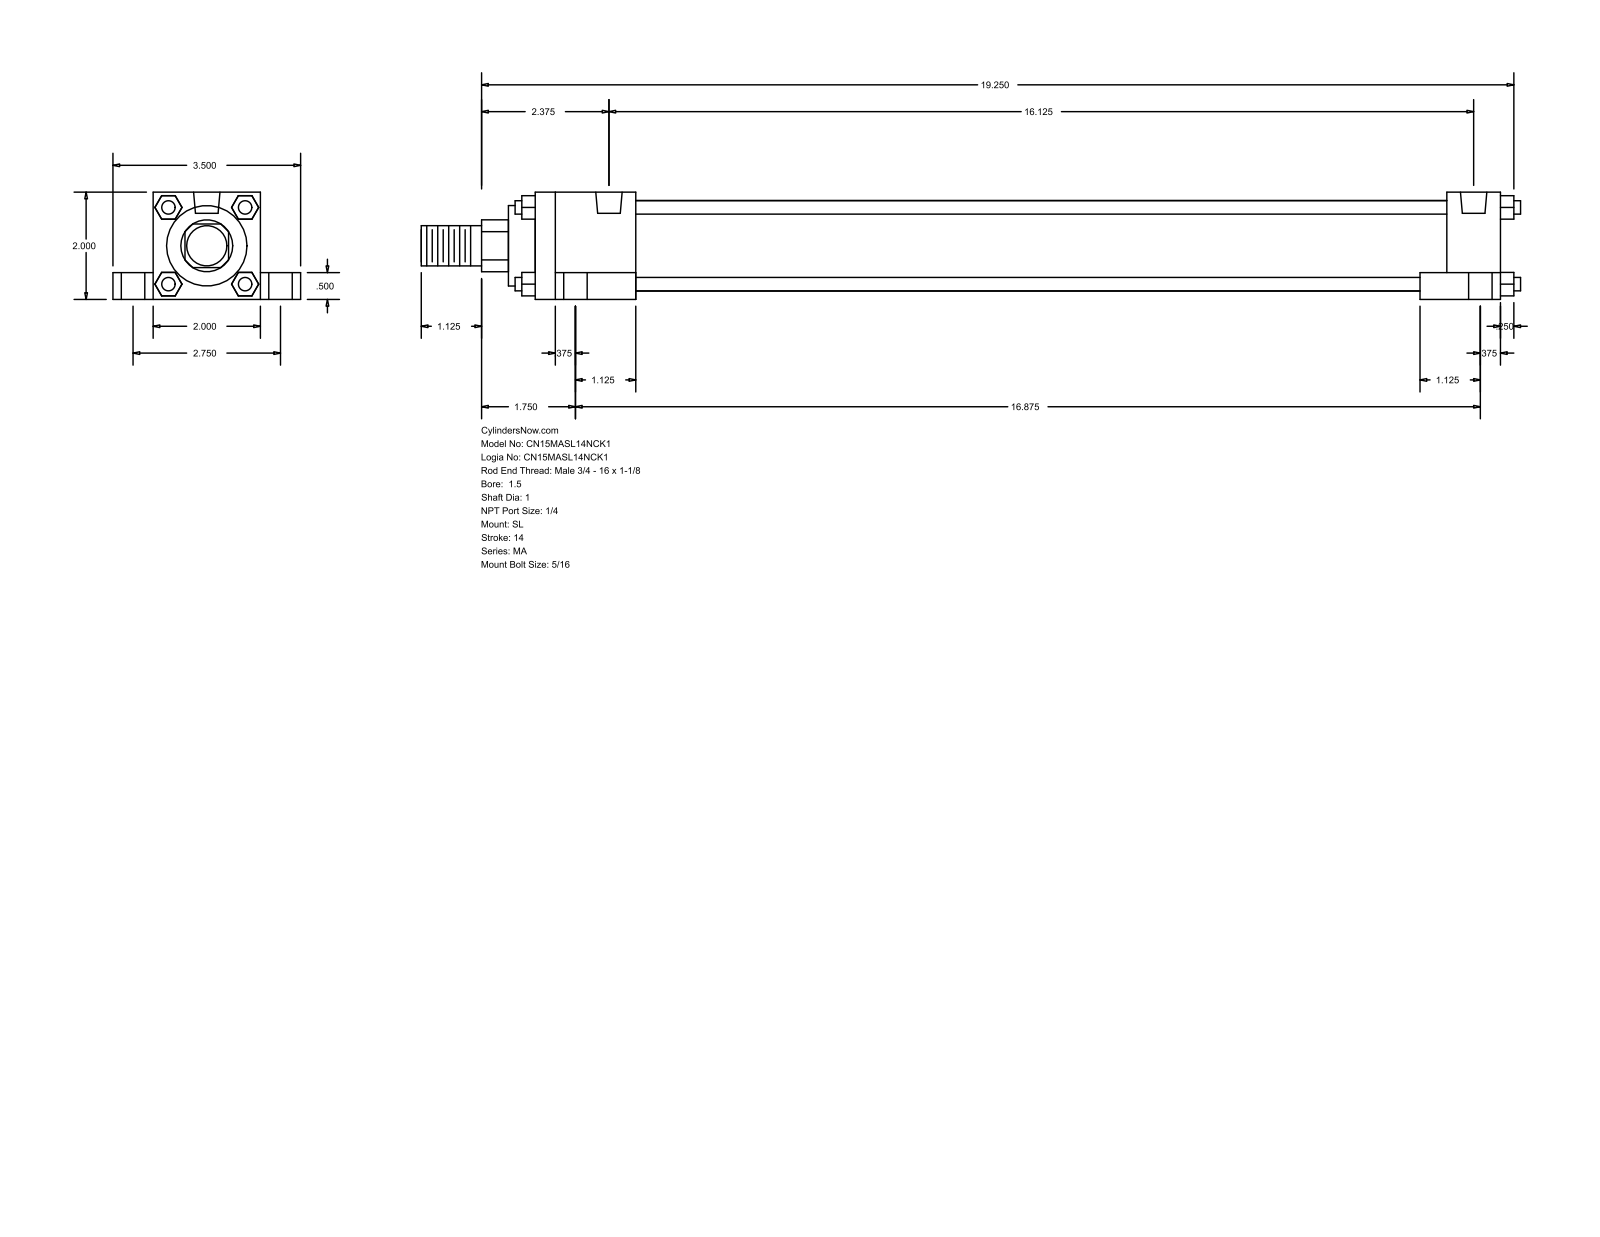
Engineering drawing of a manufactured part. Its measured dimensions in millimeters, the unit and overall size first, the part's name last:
Units: millimetres
Overall size (bounding box): 520.7 × 88.9 × 50.8
Round holes (diameter × count): ⌀7.94 ×4, ⌀11.11 ×4, ⌀17.46 ×4, ⌀12.49 ×2
Round bosses / shafts (diameter × count): ⌀6.35 ×4, ⌀42.93 ×1, ⌀38.1 ×1, ⌀25.4 ×1, ⌀19.05 ×1
Partial cylindrical surfaces — rounded edges, fillets, slot ends (radius × count): R12.29 ×1
Main face-to-face distances: 50.8, 12.7, 19.05, 69.85, 38.1, 9.52, 457.2, 25.4, 6.35, 431.8
Hole centre spacings: 35.06, 38.36, 69.84, 409.57, 414.21, 426.88, 428.62, 434.27
Bodies: 0 solids, 148 faces (112 planar, 36 cylindrical, 0 other)
Part name (STEP PRODUCT): MA_SL__0150_1
STEP written by: GSSL Pune (CONFIG_CONTROL_DESIGN)
